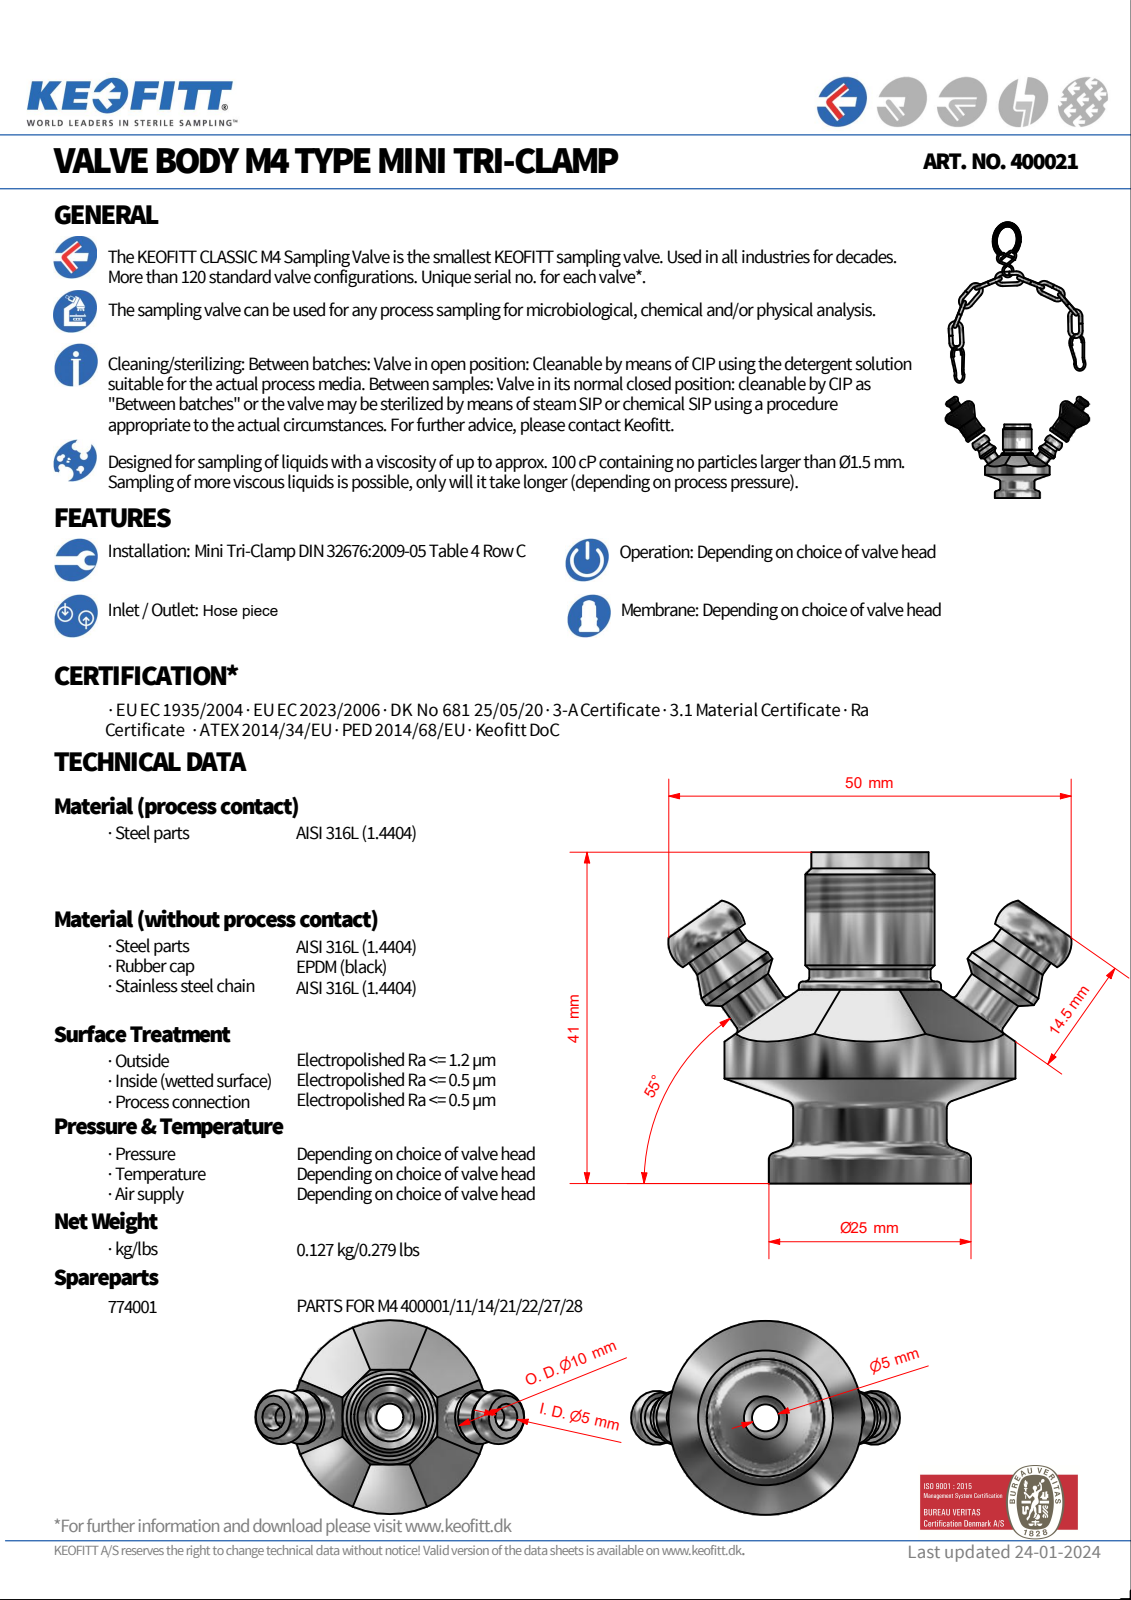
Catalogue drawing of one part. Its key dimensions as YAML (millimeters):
step_written_by: "Autodesk Inventor 2008 (AUTOMOTIVE_DESIGN)"
units: millimeters
bodies: {solids: 95, faces: 351, planar: 95, cylindrical: 82, other: 174}
overall_size: [143.32, 68.35, 48.45]
volume: 25349
surface_area: 11609
round_holes:
  - {diameter: 2, count: 9}
  - {diameter: 3.5, count: 2}
  - {diameter: 5, count: 1}
  - {diameter: 13.2, count: 1}
round_bosses_or_shafts:
  - {diameter: 2, count: 21}
  - {diameter: 11, count: 2}
  - {diameter: 10, count: 2}
  - {diameter: 7, count: 2}
  - {diameter: 6.5, count: 2}
  - {diameter: 5.6, count: 2}
  - {diameter: 5, count: 2}
  - {diameter: 4, count: 2}
partial_cylinders:
  - {radius: 0.1, count: 9}
face_to_face_distances: [25.61, 0.7, 25, 24.3, 18.61, 7, 6.61, 12, 19, 16]
